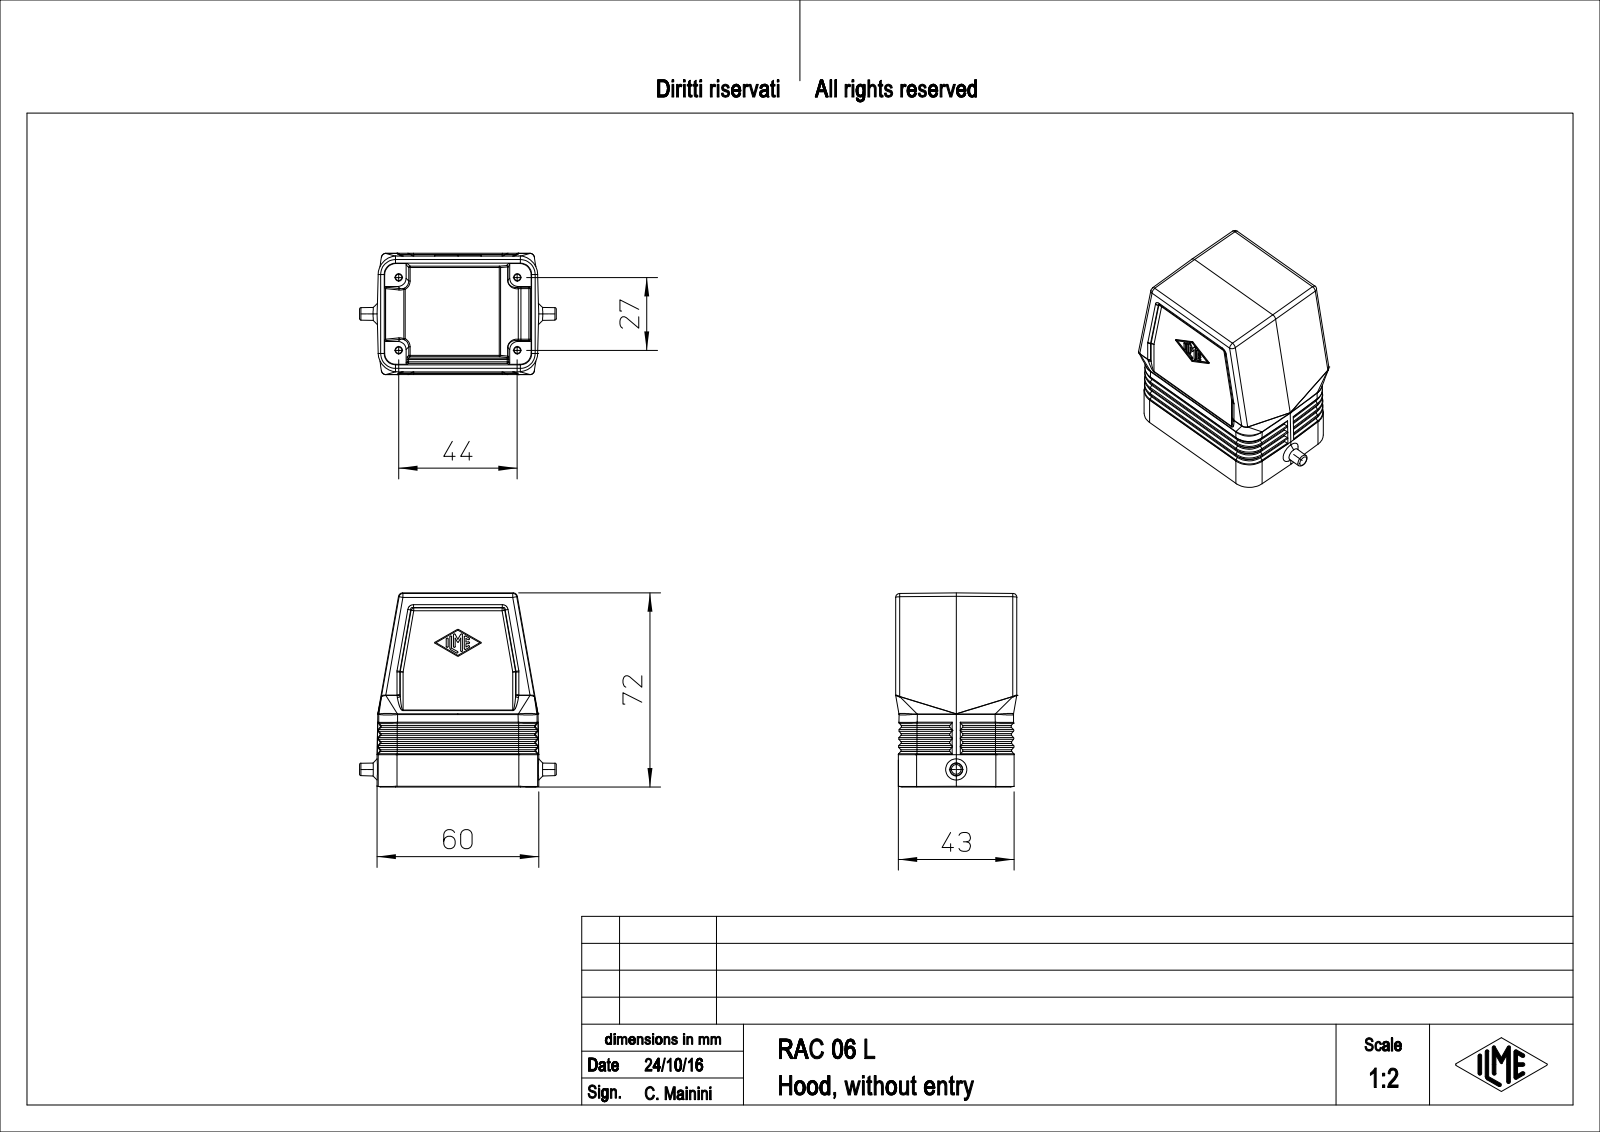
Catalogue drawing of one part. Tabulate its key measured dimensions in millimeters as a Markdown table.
| quantity | value |
| --- | --- |
| part name | RAC_06_L |
| STEP written by | PTC Creo Elements/Direct Modeling 19.0E 27-Jun-2016 (C) Parametric Technology GmbH (AUTOMOTIVE_DESIGN) |
| units | millimeters |
| bodies | 1 solid, 378 faces (154 planar, 100 cylindrical, 124 other) |
| overall size | 73 × 72 × 45 |
| volume | 62 668 mm³ |
| surface area | 29 354 mm² |
| round holes (diameter × count) | 2.75 × 4 |
| round bosses / shafts (diameter × count) | 4.62 × 1 |
| partial cylindrical surfaces (radius × count) | 0.5 × 54, 1.5 × 10, 7 × 8, 3 × 4, 4.2 × 4 |
| main face-to-face distances | 43, 1.85, 7.95, 2, 1, 44, 8.5, 4, 45, 60 |
| hole center spacings | 27, 44, 51.62 |
